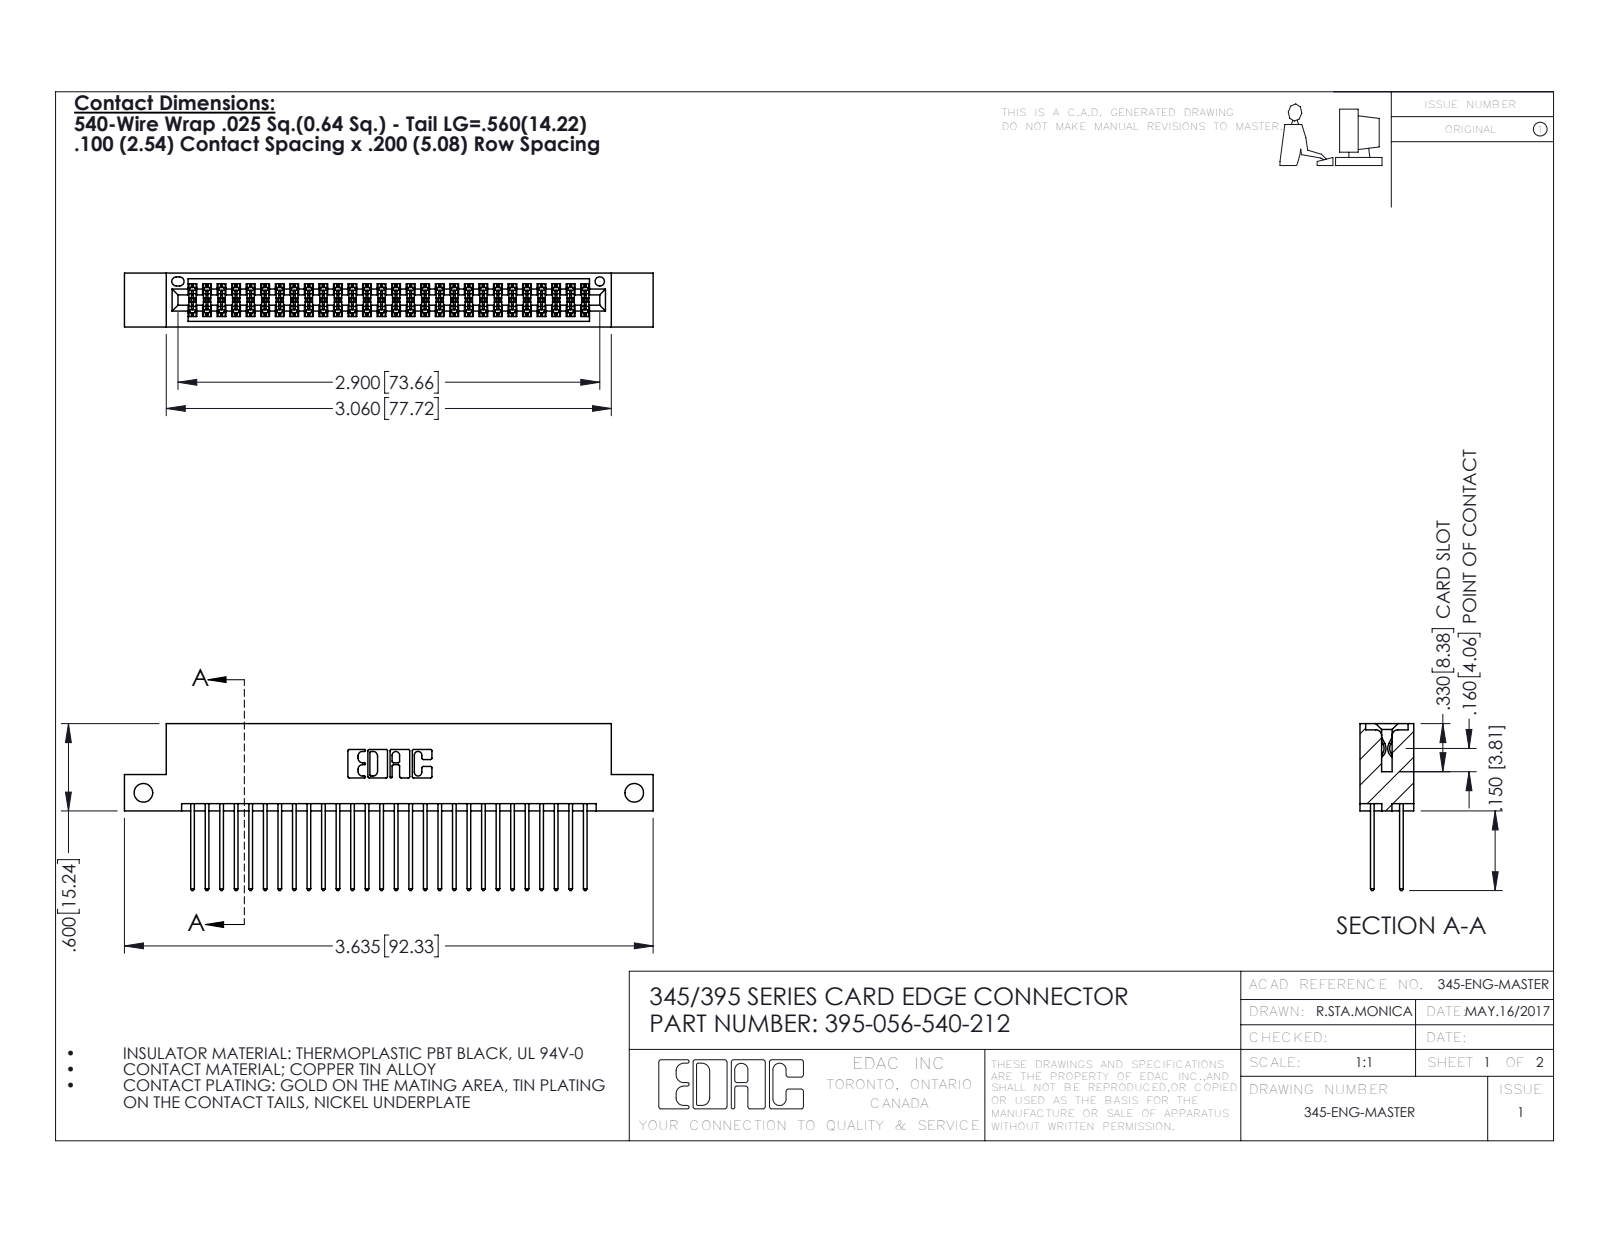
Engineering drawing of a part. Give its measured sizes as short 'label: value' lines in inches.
name: 345 Part_Flush Mounting Lugs - Side Mount; 395-056-540-212; 345-292-001_345-293-140
written by: SolidWorks 2016 (CONFIG_CONTROL_DESIGN)
unit: in
bodies: 57 solids, 2926 faces (1928 planar, 998 cylindrical, 0 other)
size: 3.635 × 1.147 × 0.37
volume: 0.547 in³; area: 21.43 in²
holes: 2× ⌀0.128, 1× ⌀0.064
rounds: 84× R0.006, 56× R0.01, 22× R0.01, 6× R0.007, 6× R0.031, 3× R0.026, 2× R0.014, 2× R0.019
face distances: 0.298, 0.072, 0.2, 0.098, 0.272, 0.025, 0.37, 0.225, 0.175, 0.149
hole spacings: 3.375
